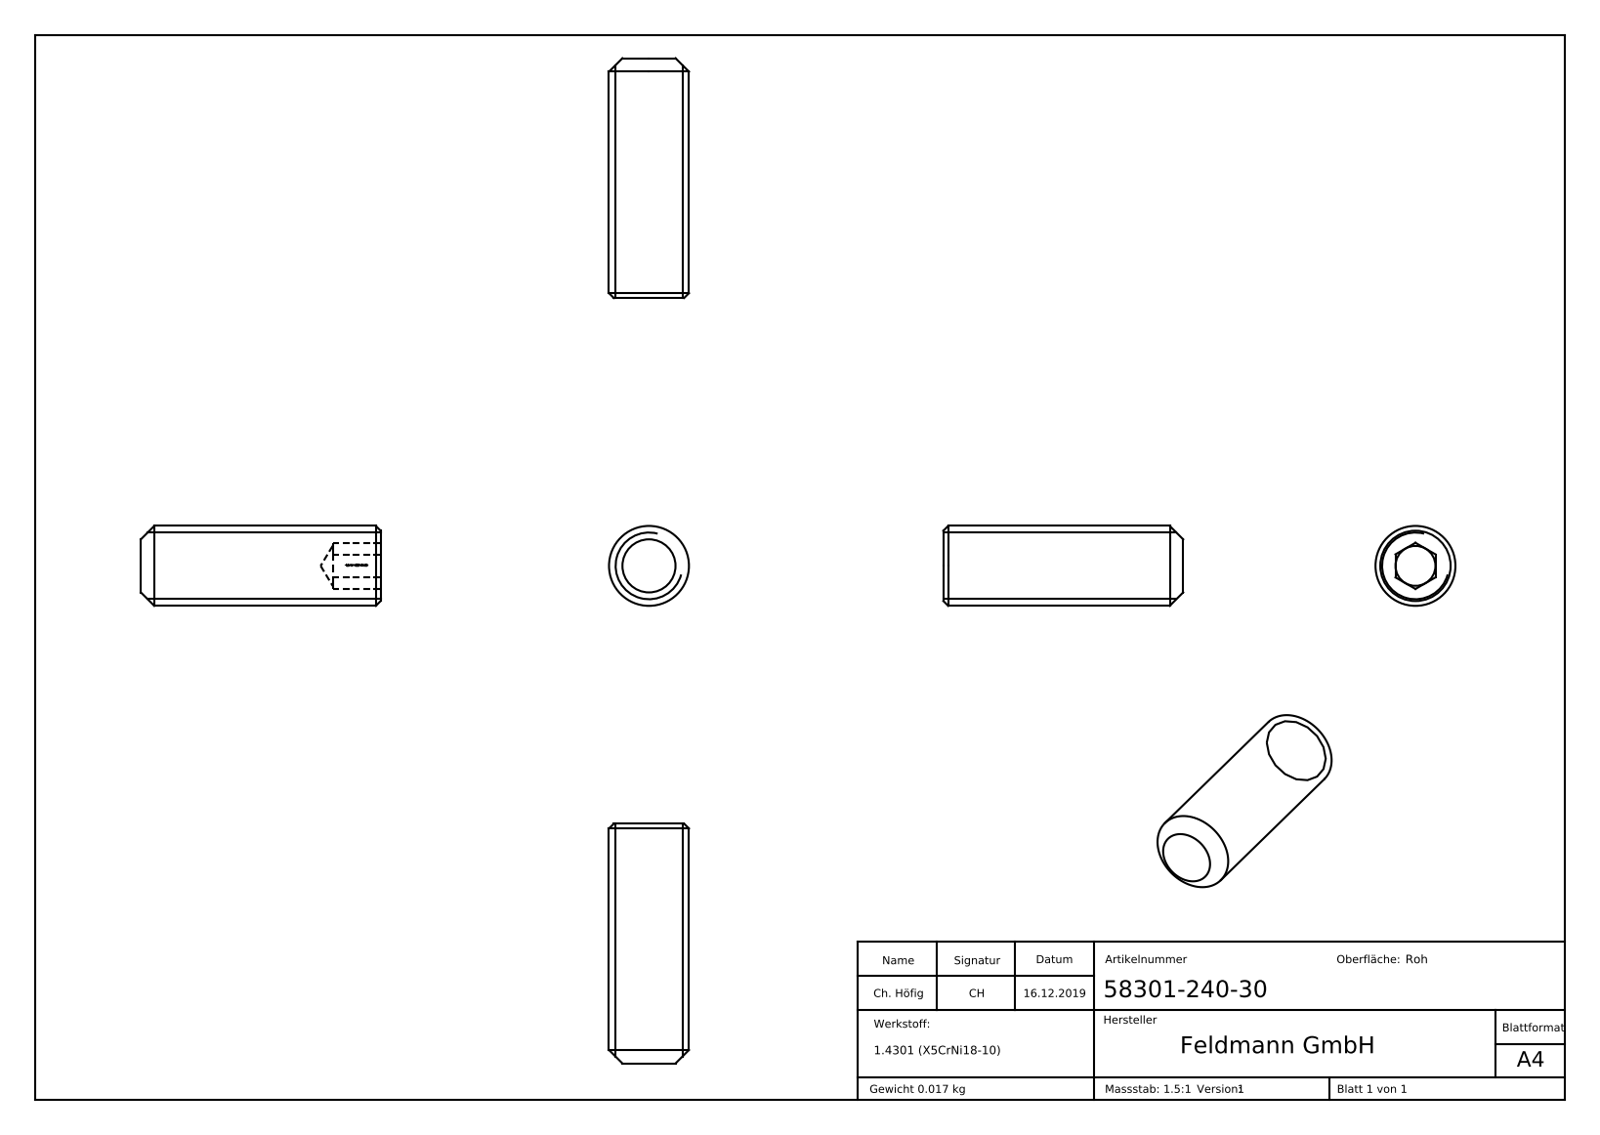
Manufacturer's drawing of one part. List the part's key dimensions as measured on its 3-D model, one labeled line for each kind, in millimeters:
Part name (STEP PRODUCT): 58301-240-30
STEP written by: SolidWorks 2015 (CONFIG_CONTROL_DESIGN)
Units: millimetres
Bodies: 1 solid, 293 faces (140 planar, 1 cylindrical, 152 other)
Overall size (bounding box): 110 × 10 × 10
Volume: 2 172 mm³ · Surface area: 1 162 mm²
Round bosses / shafts (diameter × count): ⌀10 ×1
Main face-to-face distances: 5, 30, 24, 6, 5.1, 0.37, 0.48, 0.54, 0.82, 0.96
